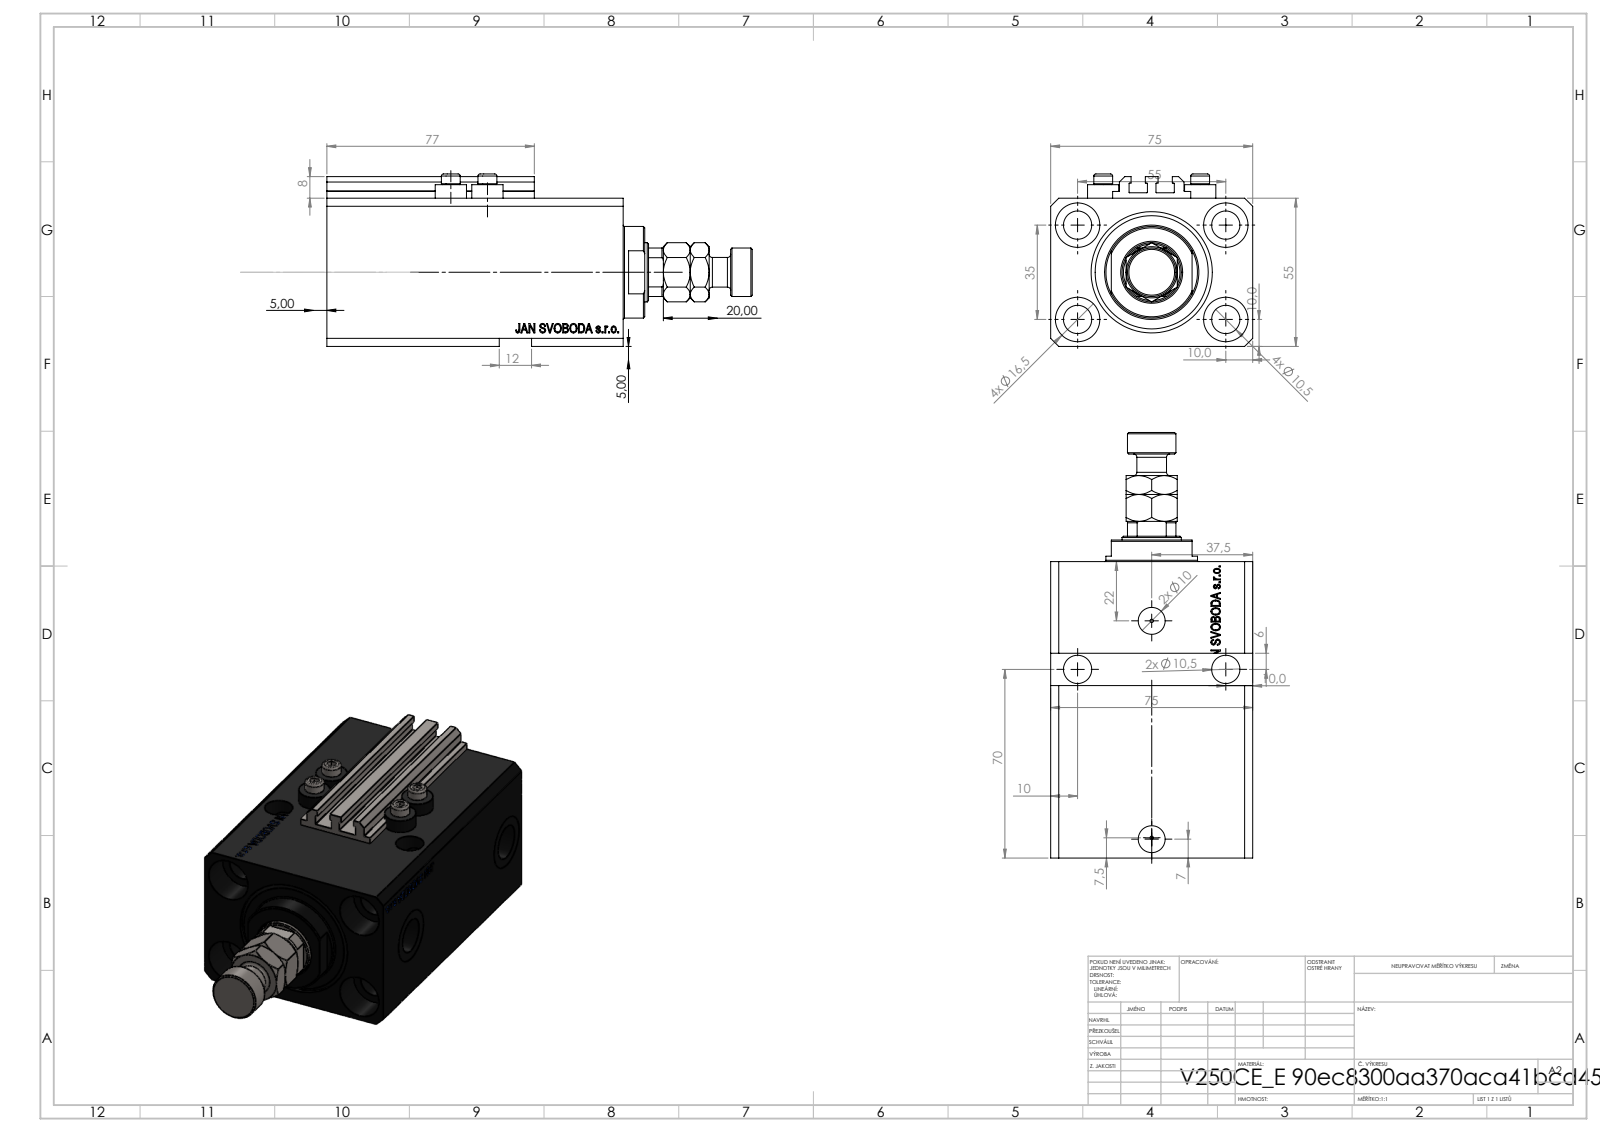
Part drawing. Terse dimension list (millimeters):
name: V250CE_C_VCP; V250CE_VC_E; MFA; ALLEN BOLT V250CE (+1 more)
written by: SolidWorks 2019 (CONFIG_CONTROL_DESIGN)
unit: mm
bodies: 9 solids, 1136 faces (530 planar, 150 cylindrical, 456 other)
size: 158 × 75 × 64
volume: 389 405 mm³; area: 98 340 mm²
holes: 9× ⌀10.5, 4× ⌀1.25, 4× ⌀4, 4× ⌀16.5, 2× ⌀10, 2× ⌀13.16, 2× ⌀20, 1× ⌀22, 1× ⌀32, 1× ⌀45
bosses: 4× ⌀11.6, 4× ⌀7, 1× ⌀34, 1× ⌀18, 1× ⌀11
rounds: 10× R0.2, 1× R10.5
face distances: 55, 75, 15, 110, 95, 3, 9.9, 85.1, 100.1, 2.5
hole spacings: 32.6, 32.87, 55, 68.74, 13.6, 14.09, 23.05, 25.81
